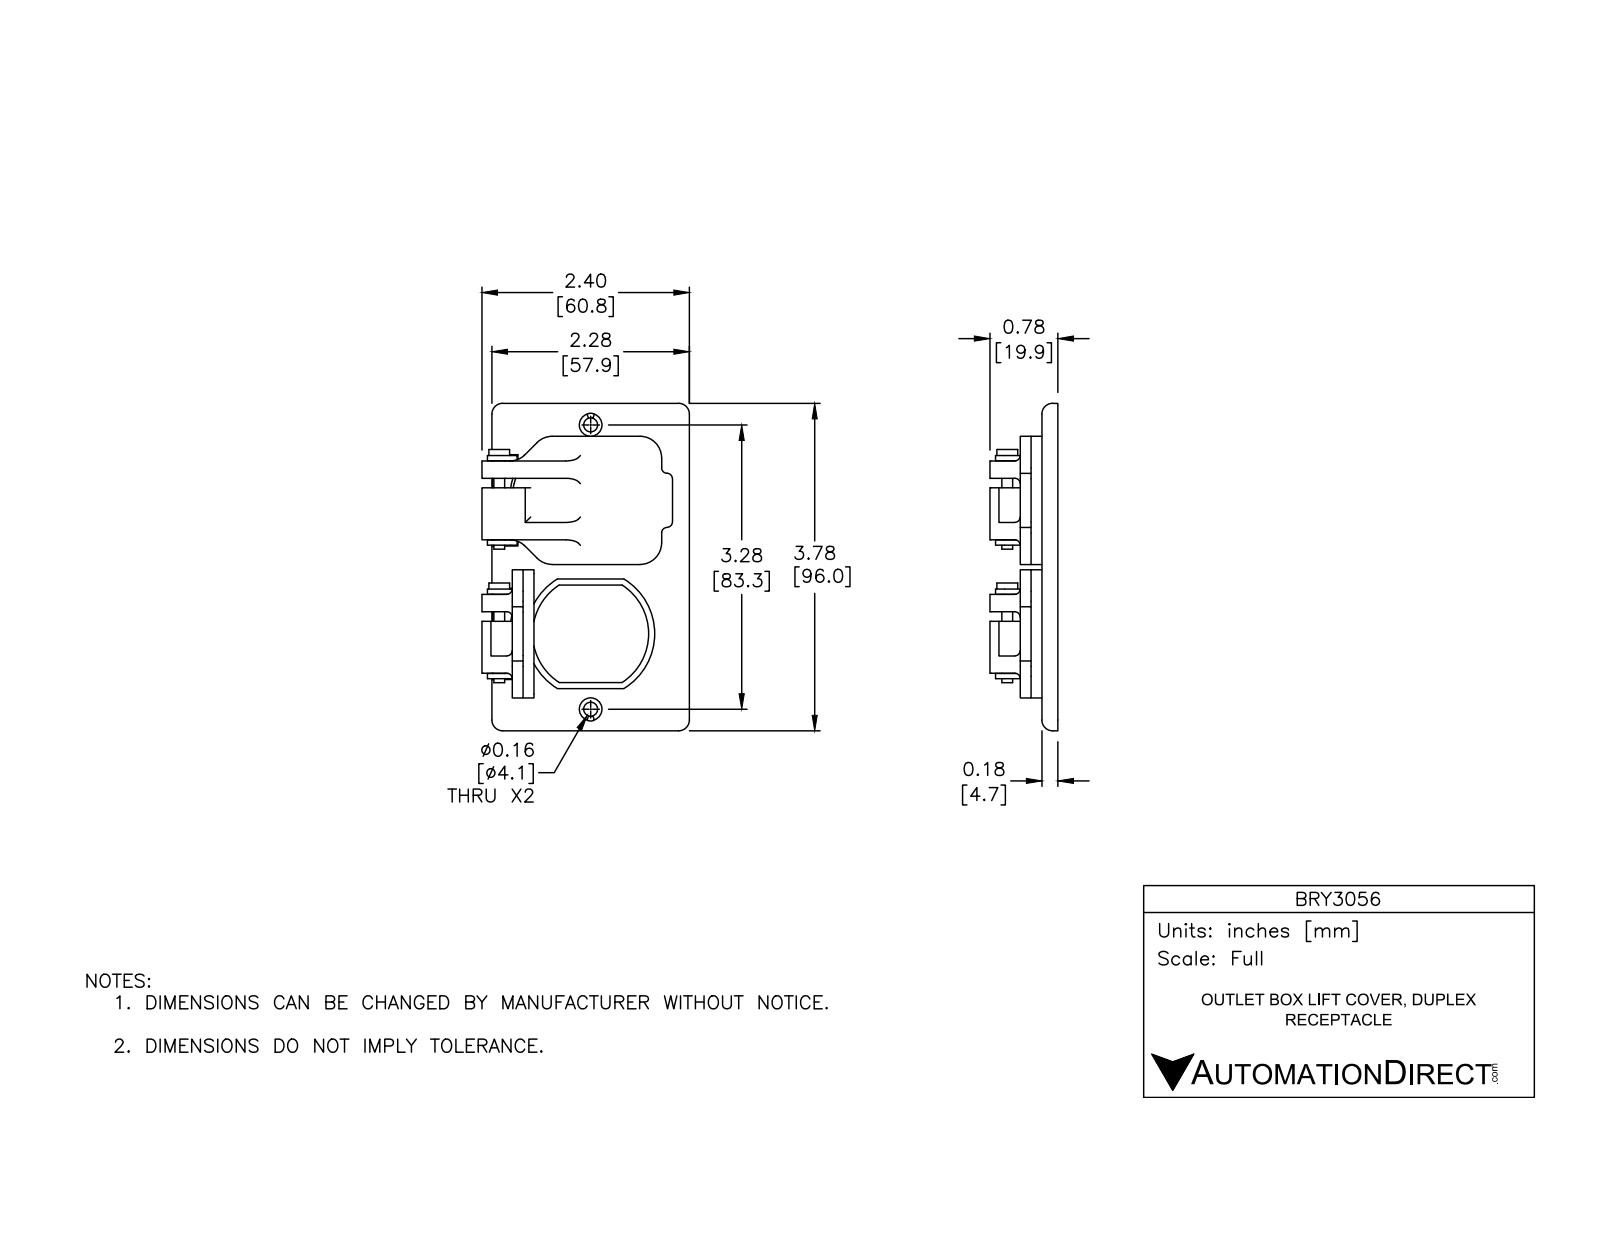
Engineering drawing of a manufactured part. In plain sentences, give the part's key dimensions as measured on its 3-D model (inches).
The part is named "BRY3056". Its 3-D file was written by "SolidWorks 2016 (AUTOMOTIVE_DESIGN)". It is 7 solids with 297 faces: 135 planar, 154 cylindrical and 8 other. Overall it measures 3.8 by 2.395 by 0.784 inches. Its volume is 2.191 cubic inches and its surface area 40.99 square inches. Round holes: 2 of diameter 0.162, 1 of diameter 0.125, 1 of diameter 0.13. Round bosses or shafts: 2 of diameter 0.302, 1 of diameter 0.24. Partial cylindrical surfaces (rounded edges, fillets, slot ends): 16 of radius 0.25, 13 of radius 0.063, 12 of radius 0.125, 9 of radius 0.062, 4 of radius 0.03, 4 of radius 0.055, 4 of radius 0.065, 2 of radius 0.2. The main face-to-face distances are 0.125, 0.125, 0.25, 0.154, 0.279, 0.404, 0.07, 0.224, 0.055, 0.18. The hole center spacings are 3.281.
